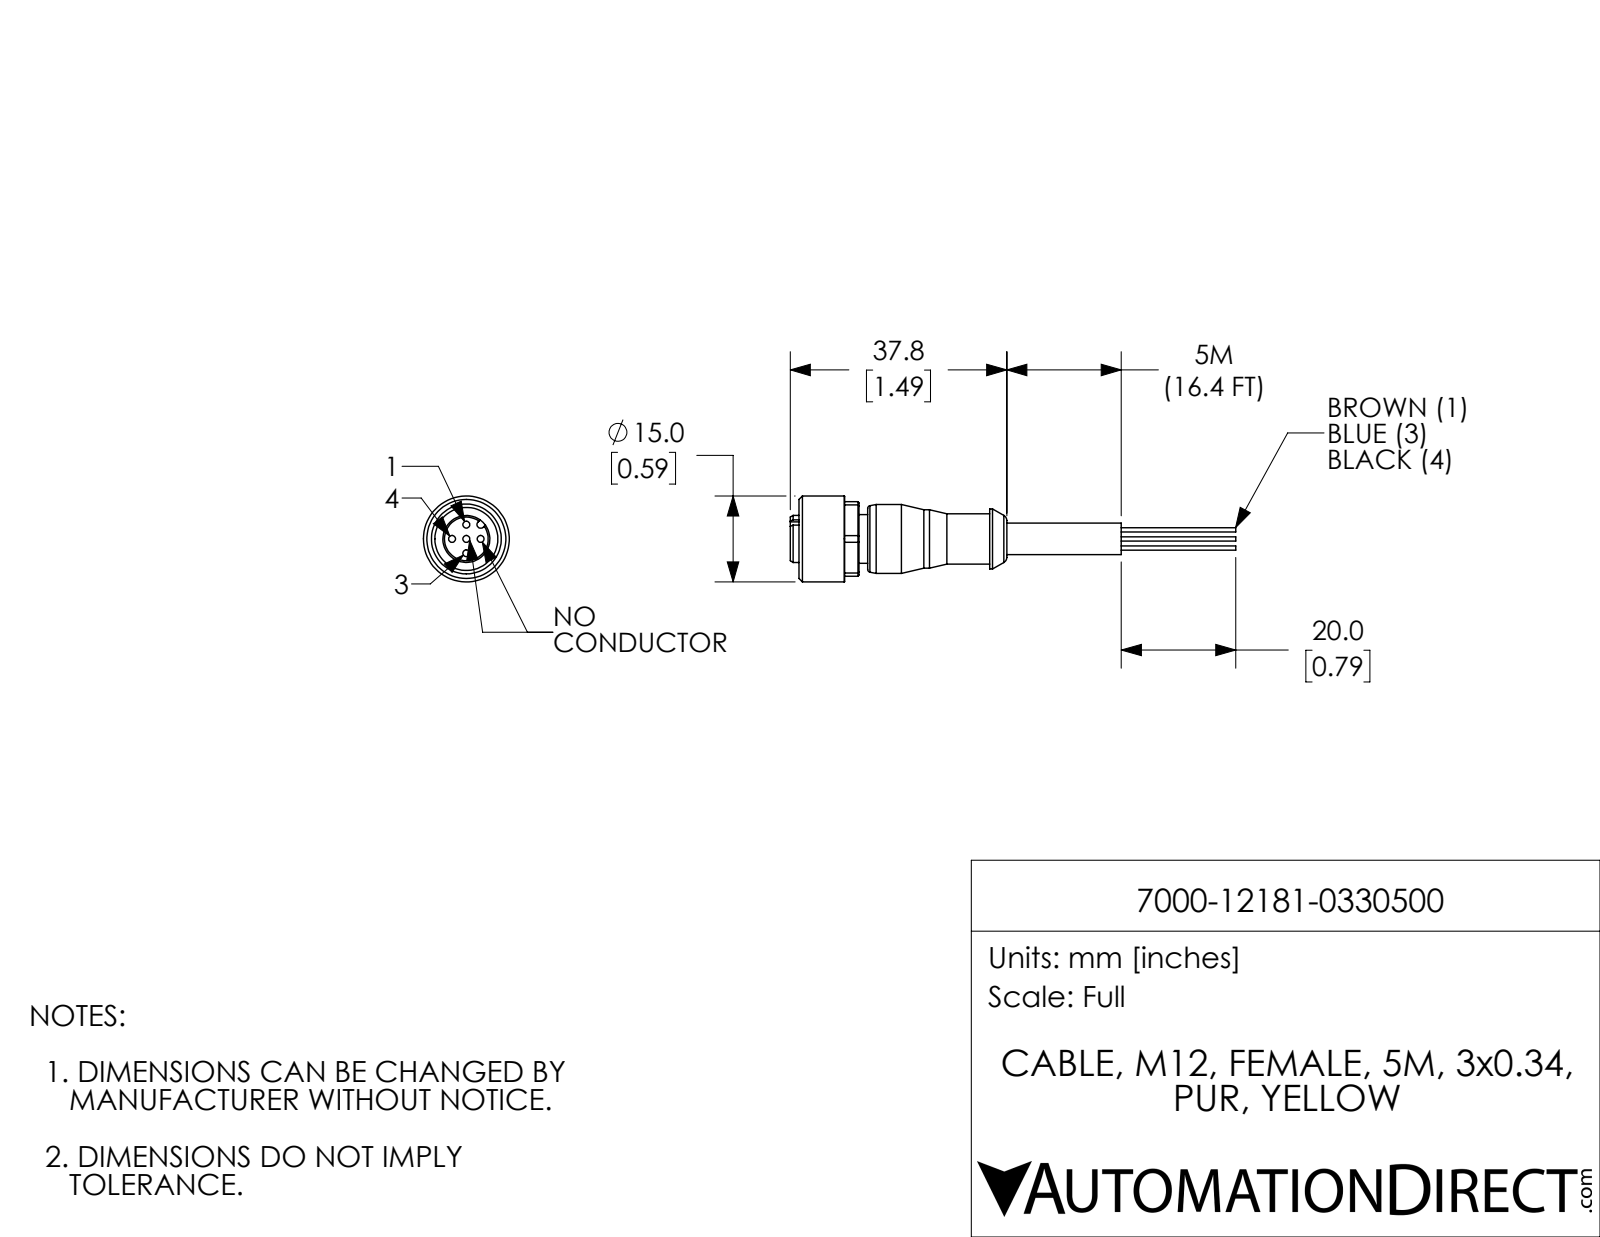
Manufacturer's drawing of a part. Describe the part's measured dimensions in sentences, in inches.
The part is named "7000-12181-0330500". Its 3-D file was written by "SolidWorks 2021 (CONFIG_CONTROL_DESIGN)". It is 1 solid with 100 faces: 32 planar, 41 cylindrical and 27 other. Overall it measures 3.063 by 0.591 by 0.591 inches. Its volume is 0.247 cubic inches and its surface area 4.356 square inches. Round holes: 5 of diameter 0.047, 1 of diameter 0.433. Round bosses or shafts: 3 of diameter 0.03, 1 of diameter 0.591, 1 of diameter 0.472, 1 of diameter 0.413, 1 of diameter 0.402, 1 of diameter 0.346, 1 of diameter 0.335, 1 of diameter 0.323. Partial cylindrical surfaces (rounded edges, fillets, slot ends): 1 of radius 0.026, 1 of radius 0.283. The main face-to-face distances are 0.472, 0.059, 0.118, 0.512, 0.354, 1.016, 0.295, 0.413, 0.098, 0.531. The hole center spacings are 0.098, 0.139, 0.197.
